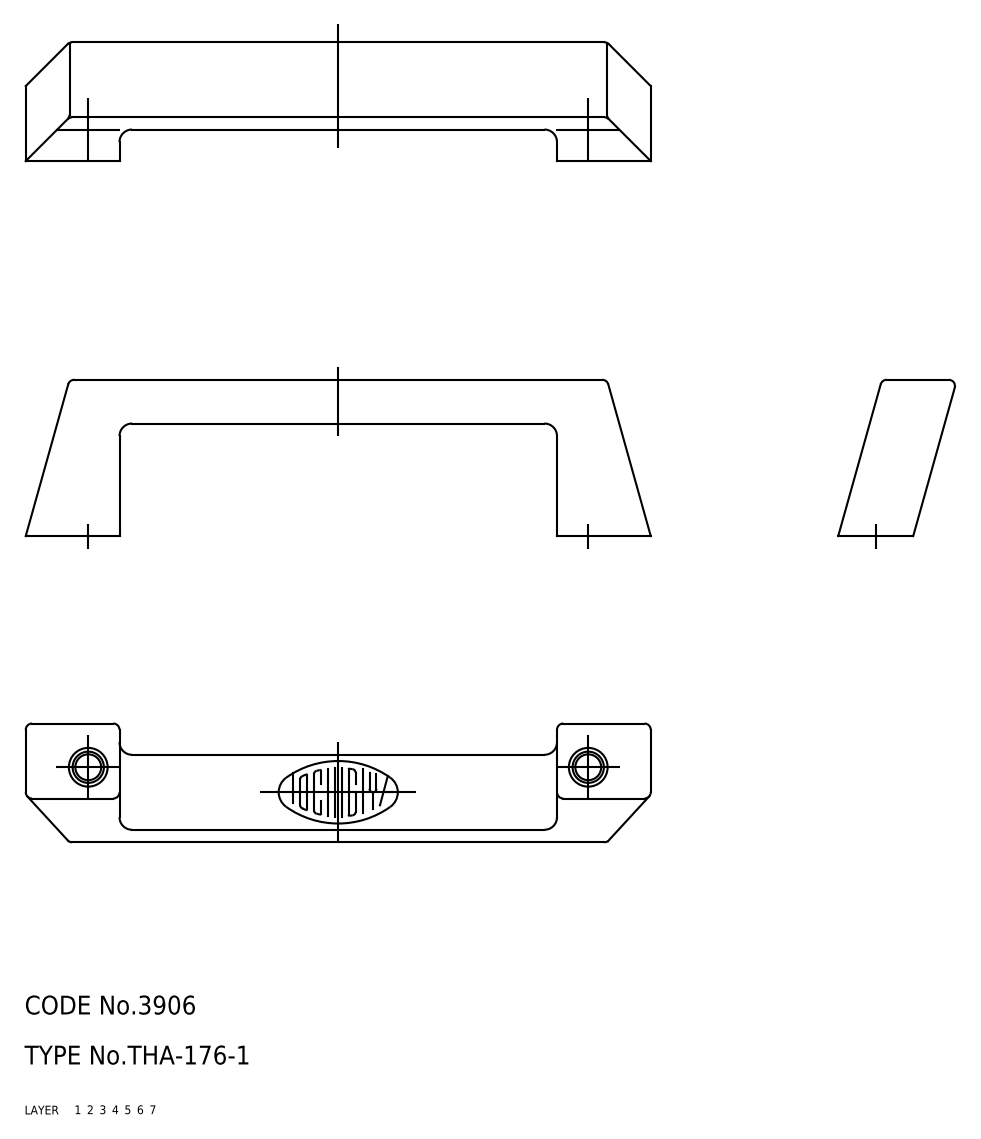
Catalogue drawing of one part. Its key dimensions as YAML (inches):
part_name: "pull"
step_written_by: "CADfix (AUTOMOTIVE_DESIGN)"
units: inches
bodies: {solids: 1, faces: 40, planar: 0, cylindrical: 0, other: 40}
overall_size: [3.937, 0.984, 0.735]
volume: 0.729
surface_area: 8.438
